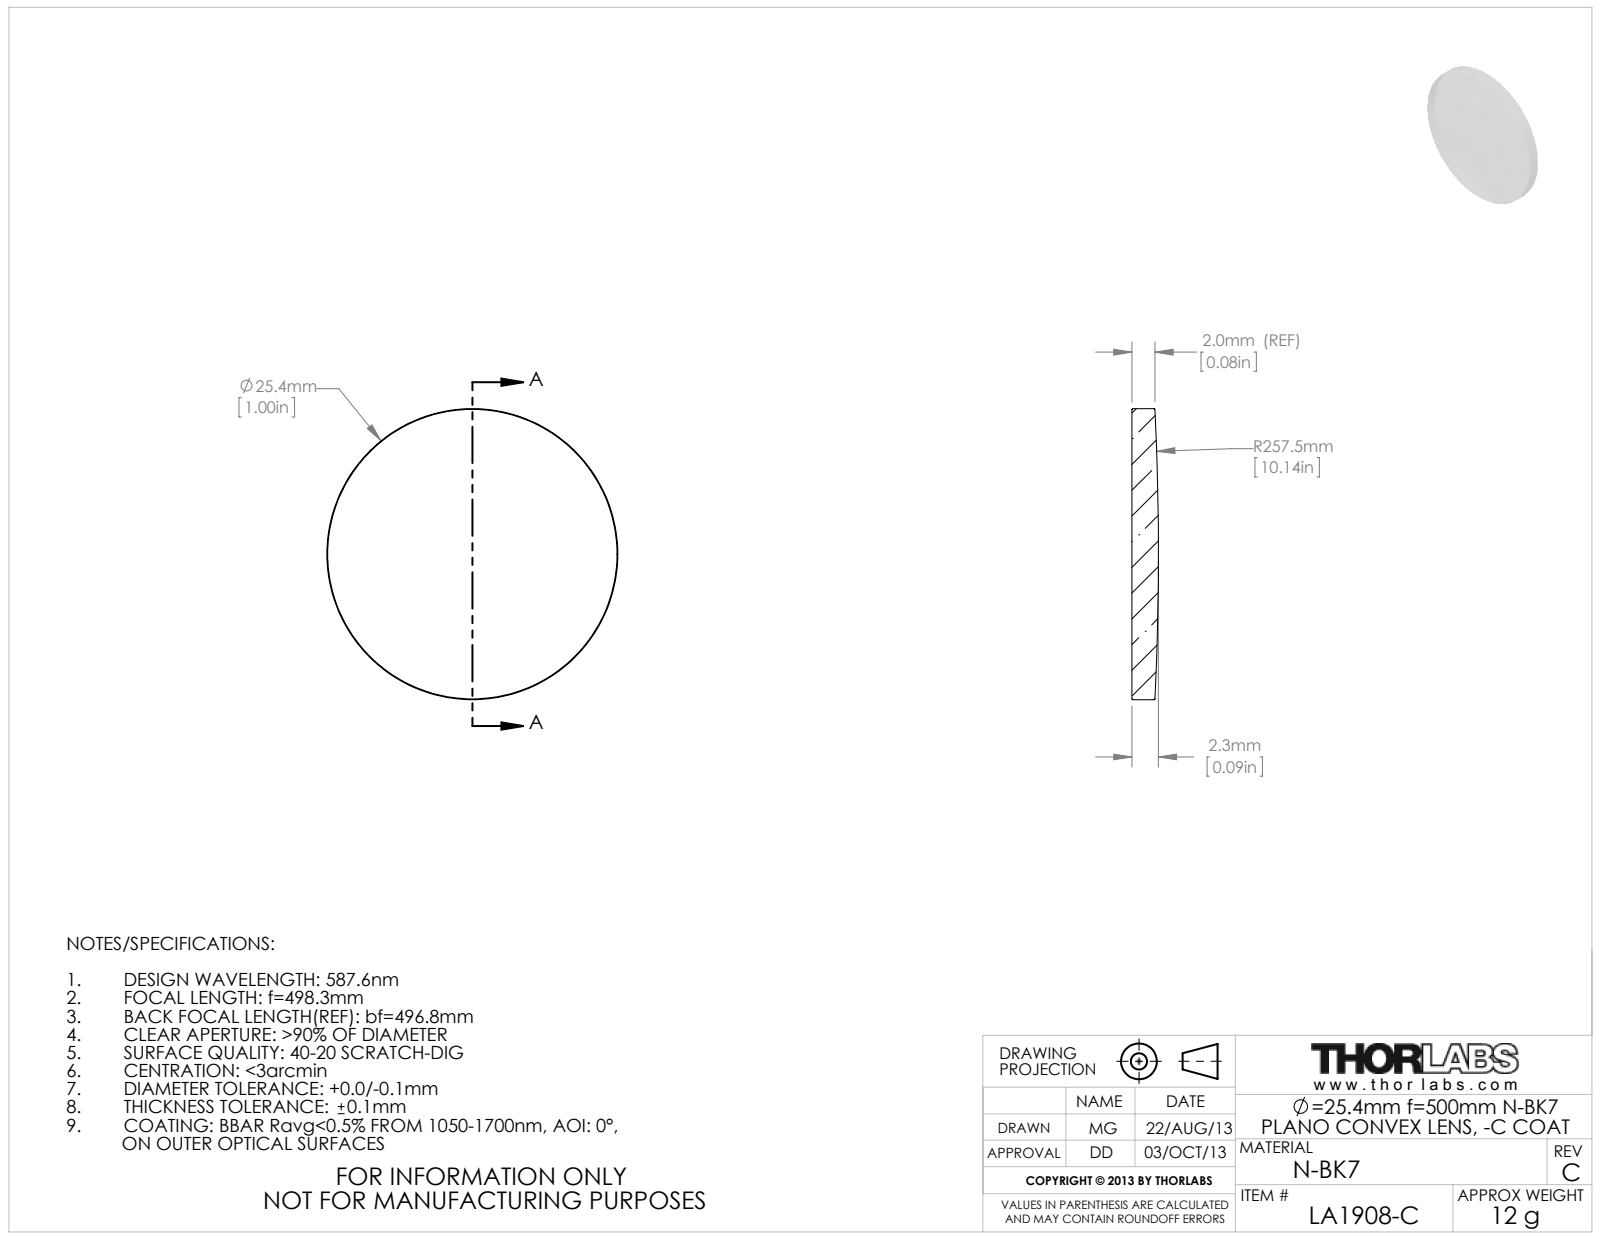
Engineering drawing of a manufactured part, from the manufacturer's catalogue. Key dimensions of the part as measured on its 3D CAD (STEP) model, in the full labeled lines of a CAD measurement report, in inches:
Part name (STEP PRODUCT): 4592-E0W
STEP written by: SolidWorks 2009 (AUTOMOTIVE_DESIGN)
Units: inches
Bodies: 1 solid, 5 faces (1 planar, 2 cylindrical, 2 other)
Overall size (bounding box): 1 × 1 × 0.091
Volume: 0.067 in³ · Surface area: 1.818 in²
Round bosses / shafts (diameter × count): ⌀1 ×1
